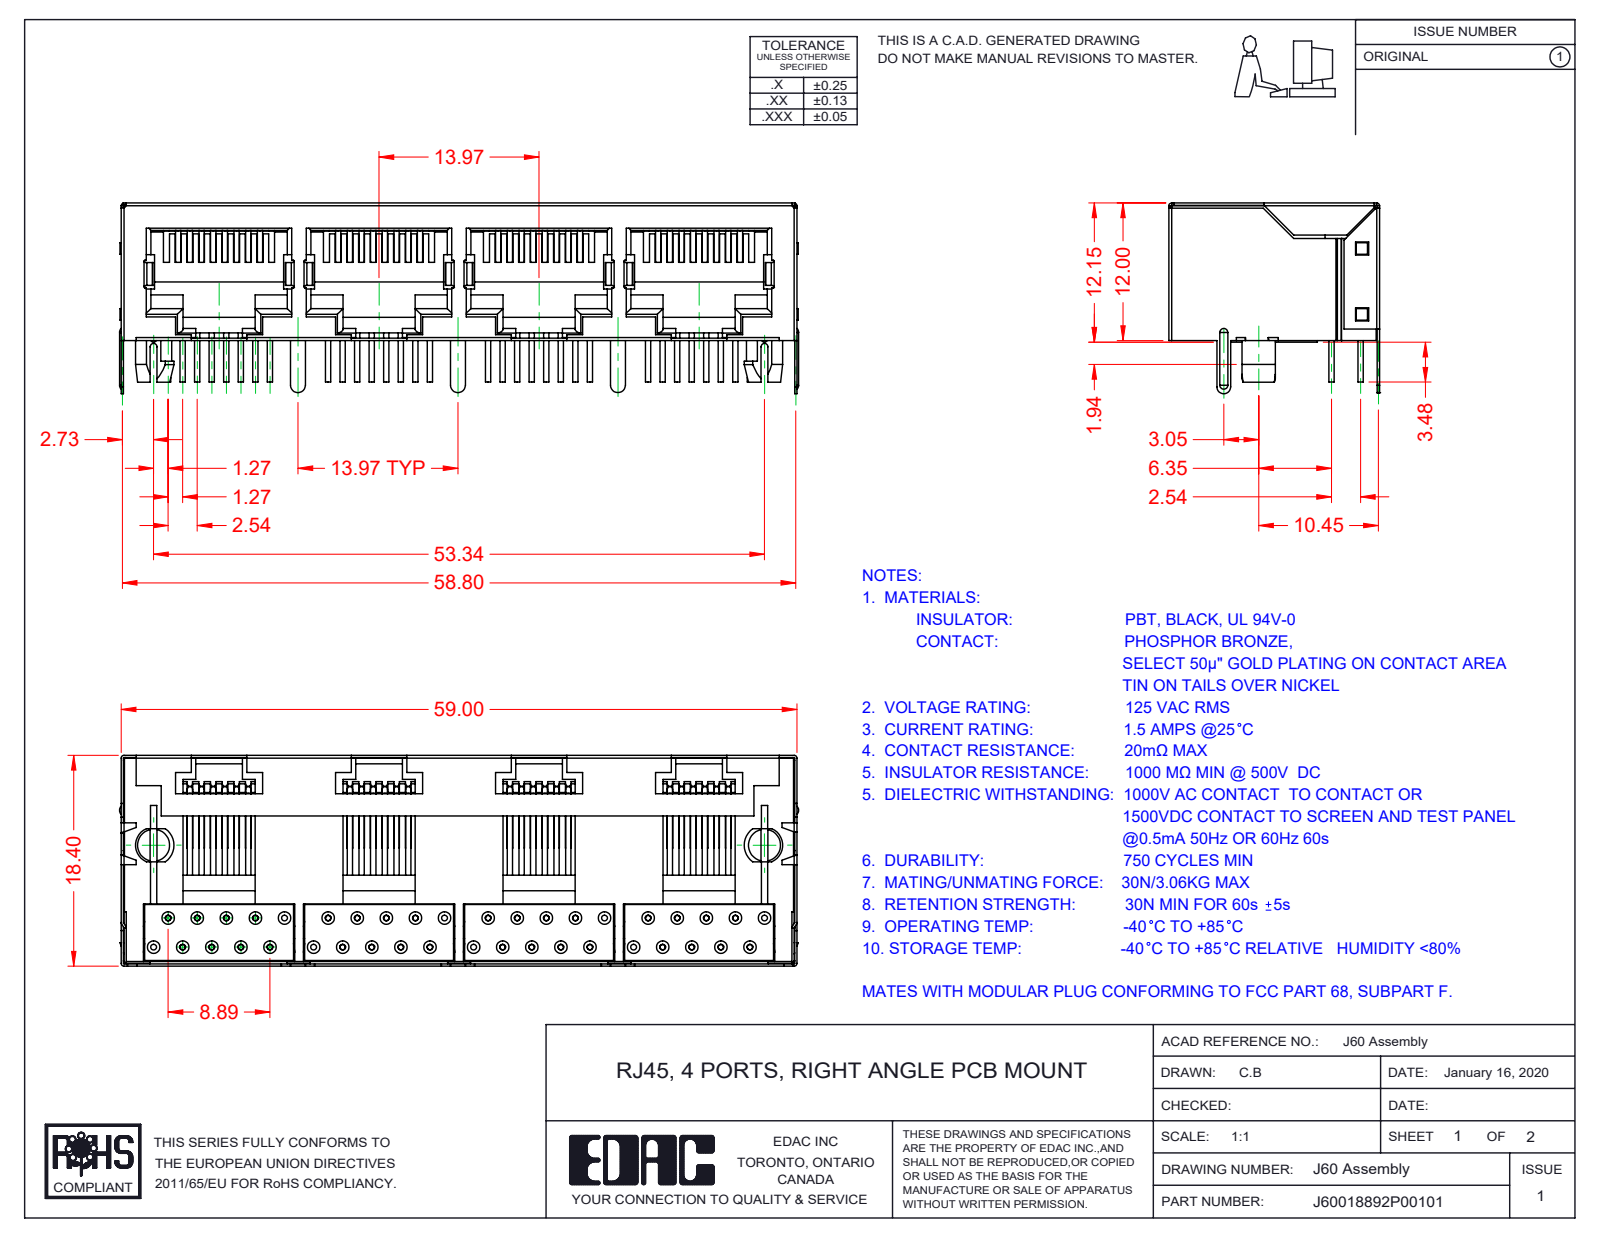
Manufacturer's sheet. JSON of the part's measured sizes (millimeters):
{"part_name": "RJ60048892P00101; 60 Contacts_8P8C; 60 Shield; 60 Insulator", "step_written_by": "SolidWorks 2016 (CONFIG_CONTROL_DESIGN)", "units": "millimeters", "bodies": {"solids": 34, "faces": 2562, "planar": 1489, "cylindrical": 715, "other": 358}, "overall_size": [59.3, 18.4, 16.65], "volume_mm3": 7013, "surface_area_mm2": 18560, "round_holes": [[0.5, 40], [1.1, 40]], "round_bosses_or_shafts": [[0.46, 96]], "partial_cylinders_radius": [[0.3, 26], [0.25, 21], [0.5, 18], [0.1, 16], [0.21, 10], [0.8, 7], [0.65, 3], [0.28, 2]], "face_to_face_distances": [0.5, 11.75, 11.55, 13.97, 2.19, 5.38, 5.18, 4.88, 18.2, 11.5], "hole_center_spacings": [2.84, 2.54, 4.58, 13.97, 5.08, 12.95, 15.45, 11.43]}
